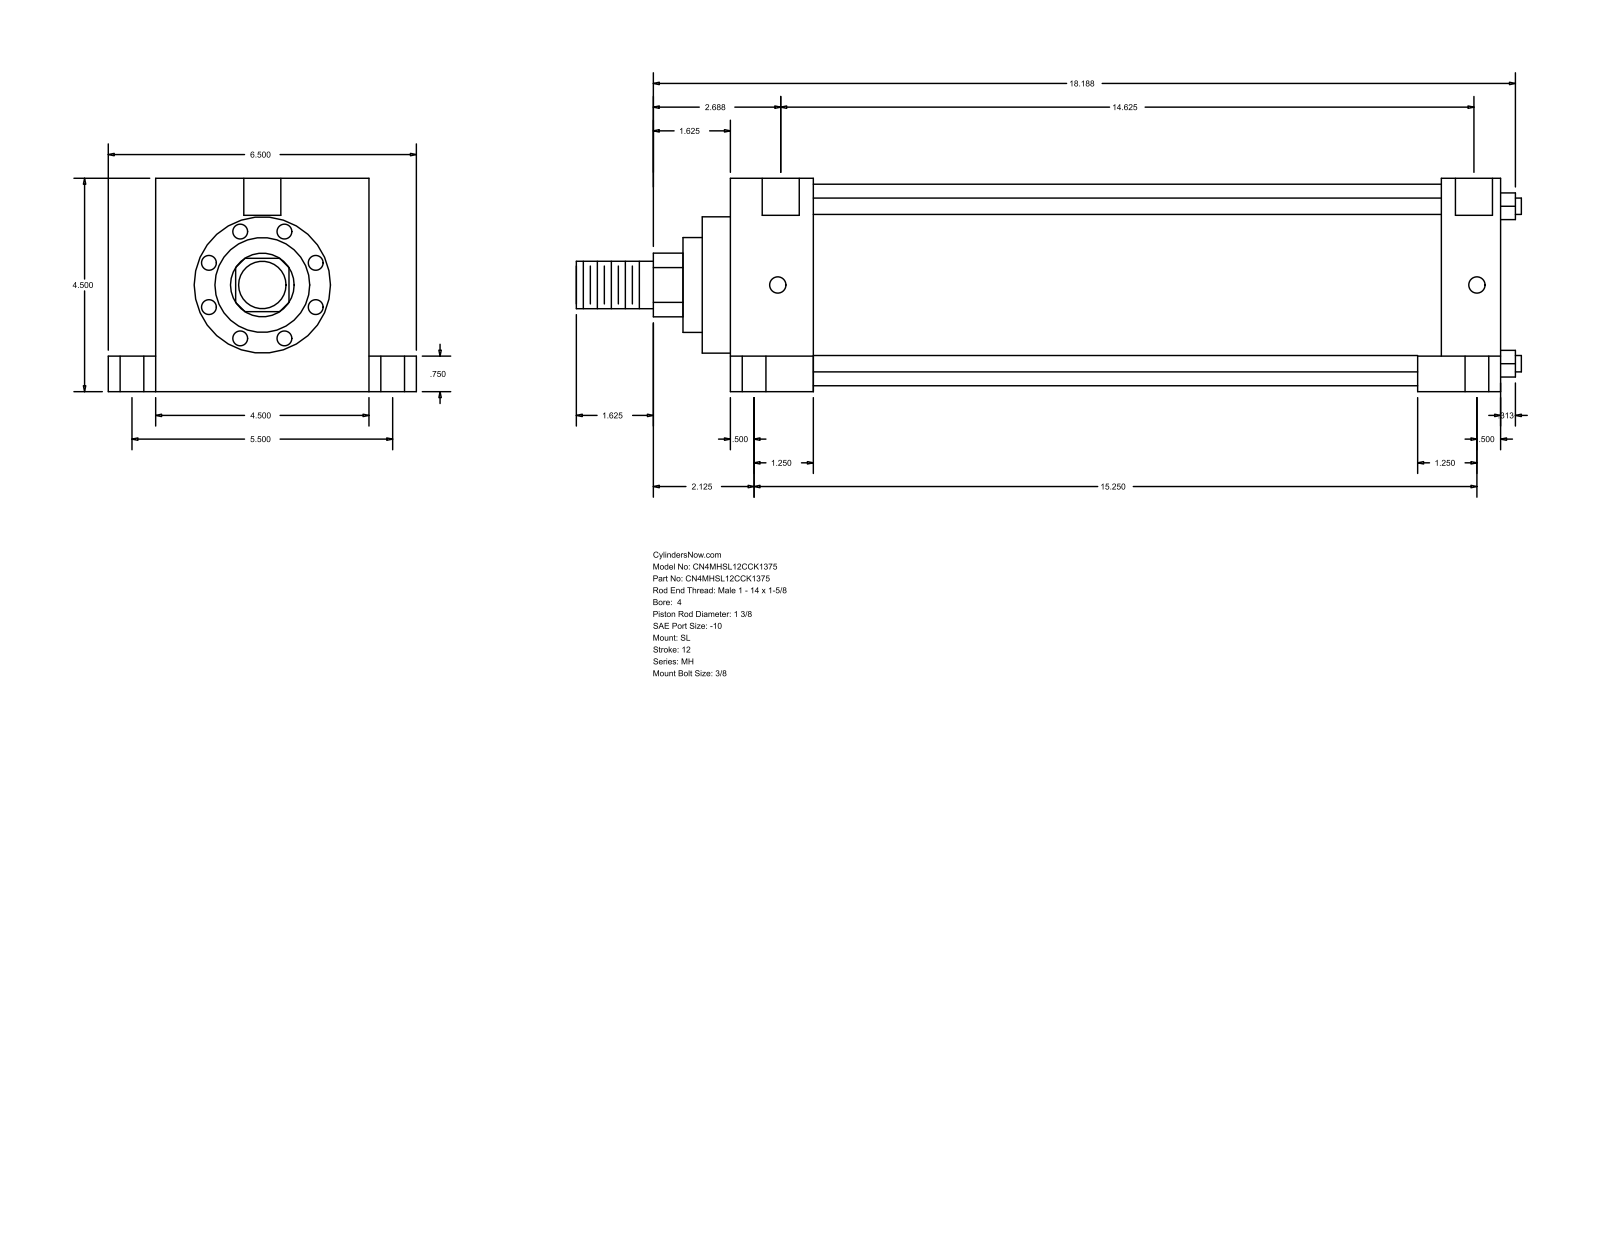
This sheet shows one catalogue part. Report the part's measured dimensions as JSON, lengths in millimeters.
{"part_name": "MH_SL__0400_1.375", "step_written_by": "GSSL Pune (CONFIG_CONTROL_DESIGN)", "units": "millimeters", "bodies": {"solids": 0, "faces": 110, "planar": 77, "cylindrical": 33, "other": 0}, "overall_size": [506.41, 165.1, 114.3], "round_holes": [[8.73, 4], [12.7, 4], [19.05, 4], [19.84, 2]], "round_bosses_or_shafts": [[8.76, 4], [107.95, 1], [73.03, 1], [50.8, 1], [34.92, 1], [25.4, 1]], "partial_cylinders_radius": [[17.06, 1]], "face_to_face_distances": [114.3, 412.75, 44.45, 368.3, 381, 336.55, 31.75, 25.4, 139.7, 19.05], "hole_center_spacings": [69.85, 69.87, 70.99, 71.29, 139.7, 374.65, 379.54, 381.11]}
